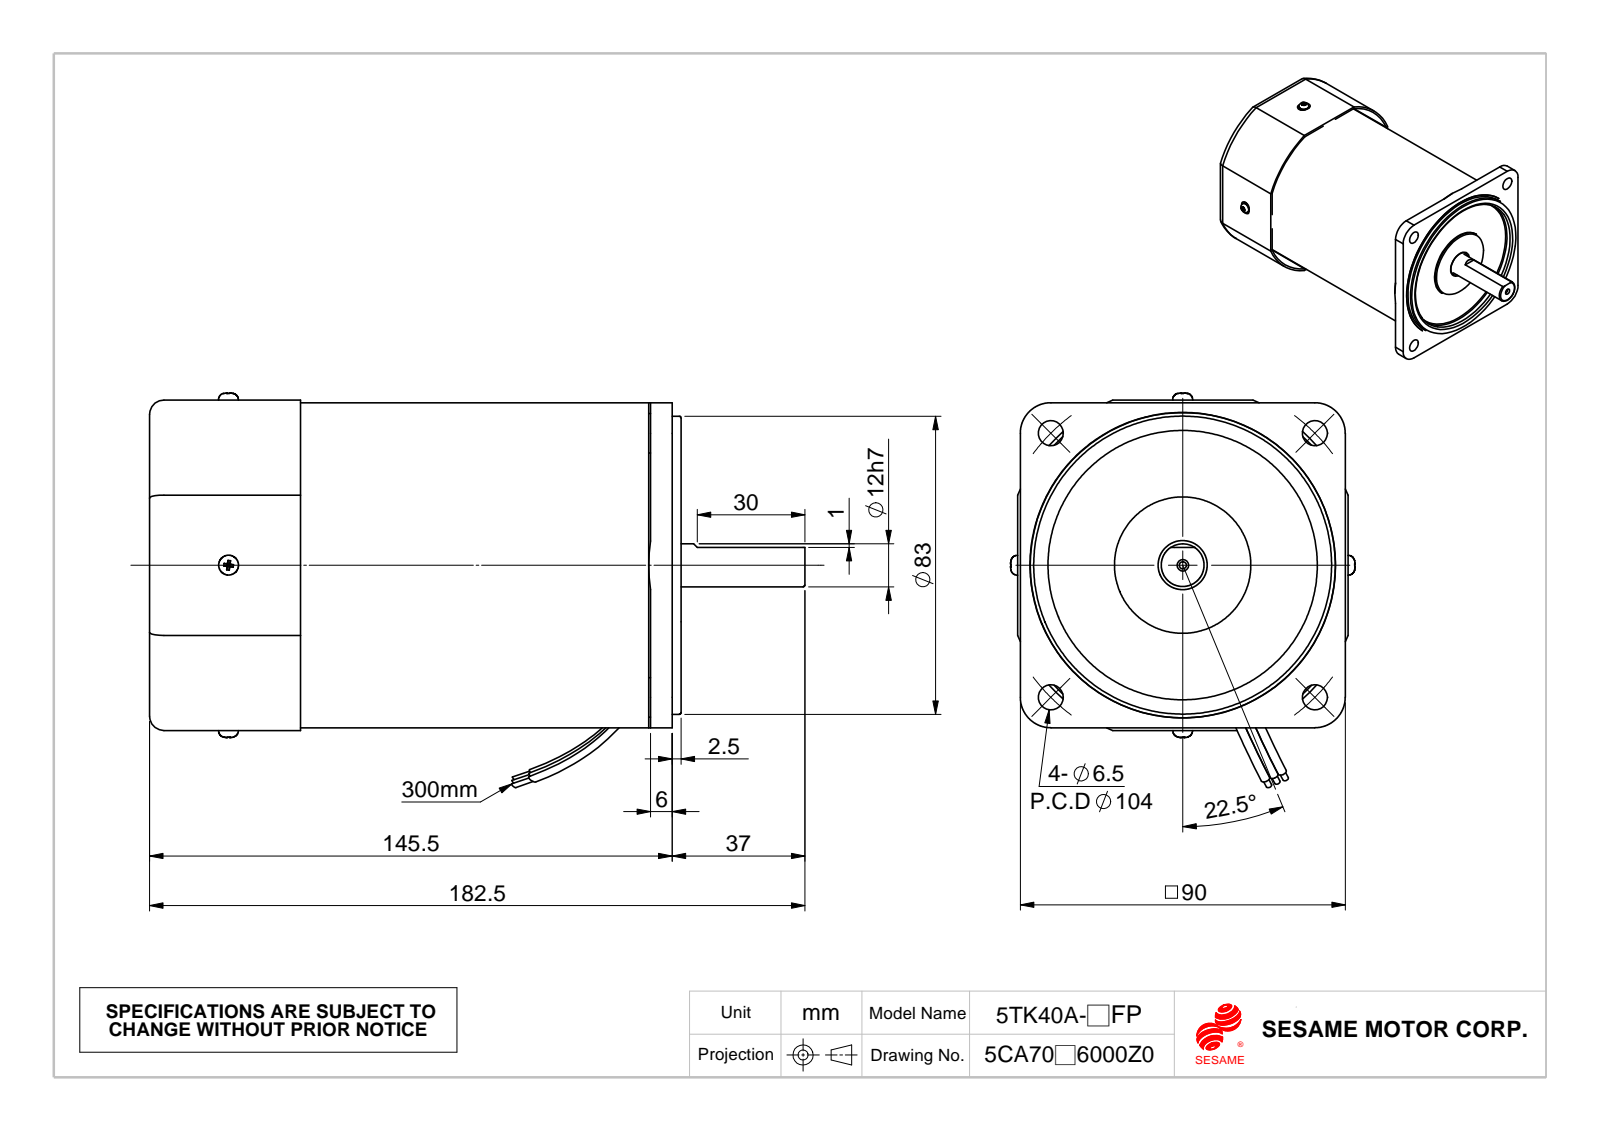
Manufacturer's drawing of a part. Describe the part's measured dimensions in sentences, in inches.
The part is named "風扇蓋FC-9042-21; 線扣; M590-F; 90A_1成品". Its 3-D file was written by "SolidWorks 2010 (CONFIG_CONTROL_DESIGN)". It is 12 solids with 509 faces: 195 planar, 202 cylindrical and 112 other. Overall it measures 7.185 by 4.326 by 3.776 inches. Its volume is 53.27 cubic inches and its surface area 174.7 square inches. Round holes: 4 of diameter 0.276, 3 of diameter 0.098, 1 of diameter 0.079, 1 of diameter 0.256, 1 of diameter 0.283, 1 of diameter 0.374, 1 of diameter 0.539, 1 of diameter 0.945, 1 of diameter 1.024, 1 of diameter 1.575, 1 of diameter 2.126, 1 of diameter 2.287. Round bosses or shafts: 3 of diameter 0.433, 2 of diameter 0.217, 2 of diameter 0.118, 1 of diameter 3.563, 1 of diameter 3.386, 1 of diameter 3.313, 1 of diameter 3.307, 1 of diameter 3.268. Partial cylindrical surfaces (rounded edges, fillets, slot ends): 16 of radius 0.012, 8 of radius 0.01, 8 of radius 0.039, 4 of radius 0.069, 4 of radius 0.079, 4 of radius 0.089, 4 of radius 0.118, 4 of radius 0.157. The main face-to-face distances are 0.039, 3.583, 0.63, 5.472, 5.626, 5.665, 5.512, 0.154, 5.669, 0.157. The hole center spacings are 2.047, 2.895, 4.094, 4.864.
